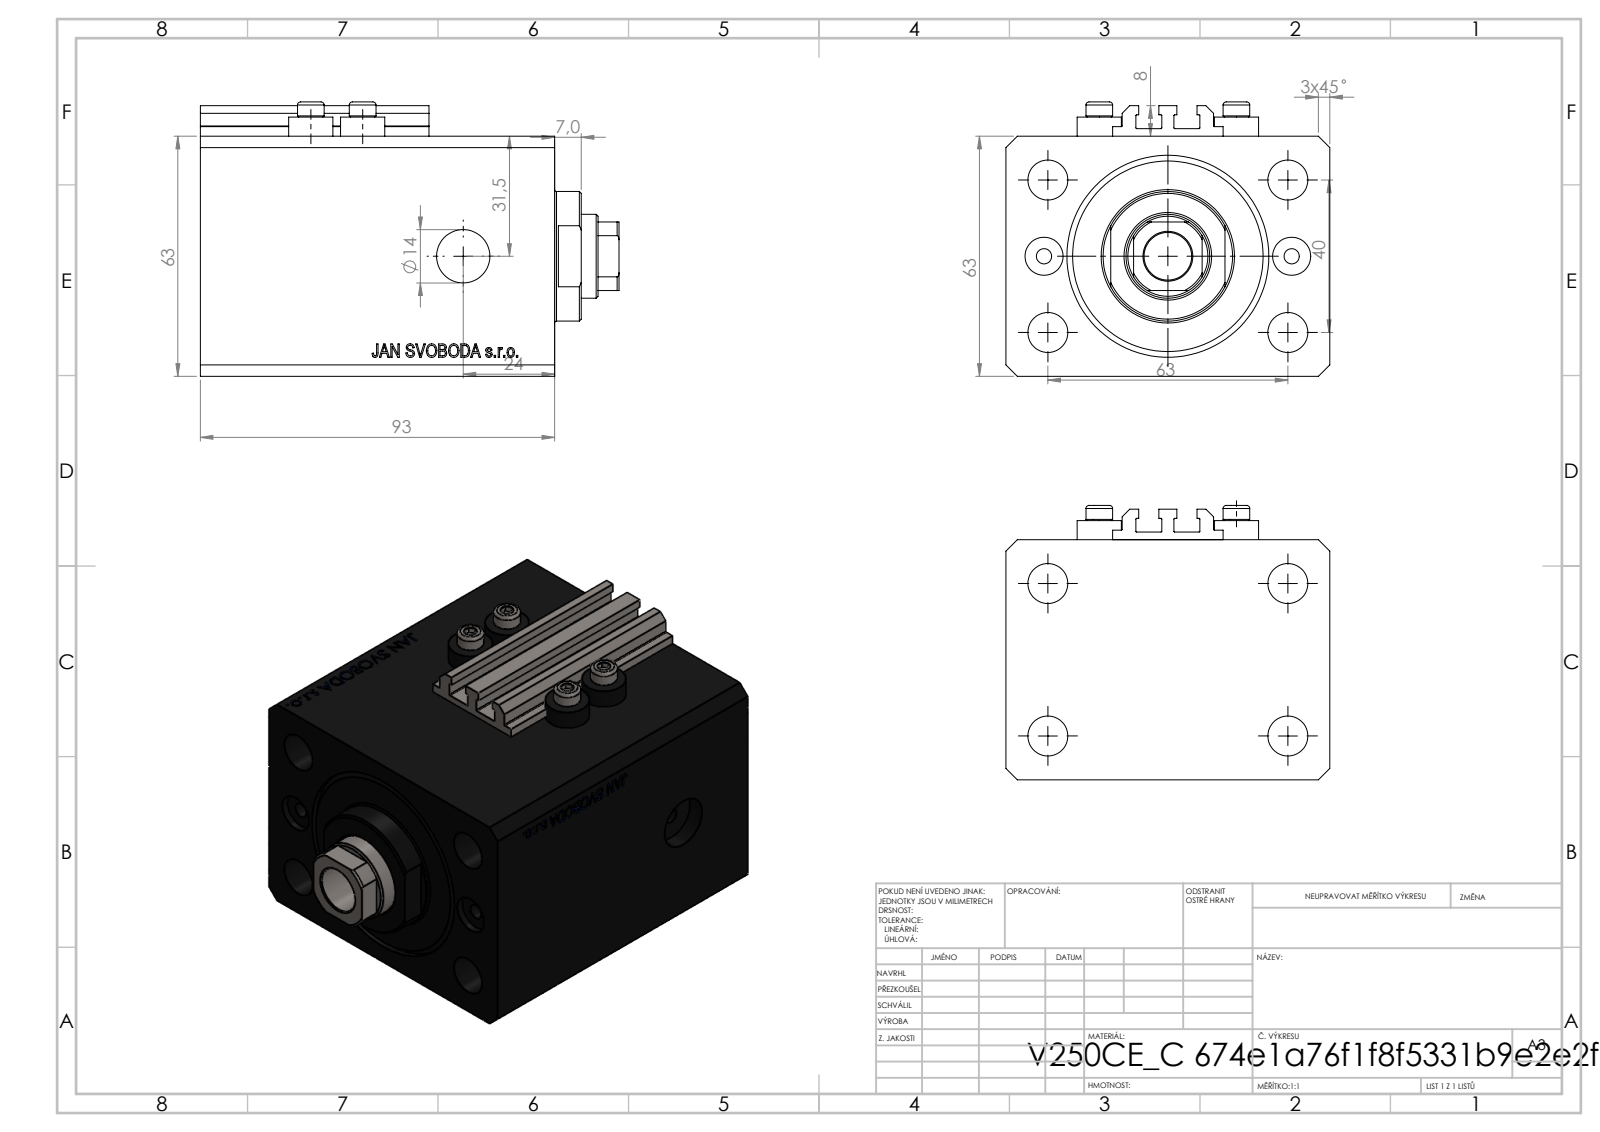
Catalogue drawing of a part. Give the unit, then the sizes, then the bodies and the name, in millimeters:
Units: millimetres
Overall size (bounding box): 110 × 85 × 72
Round holes (diameter × count): ⌀4 ×8, ⌀10.5 ×4, ⌀10 ×2, ⌀14 ×2, ⌀12.5 ×1, ⌀22 ×1, ⌀40 ×1, ⌀53 ×1
Round bosses / shafts (diameter × count): ⌀11.6 ×4, ⌀7 ×4, ⌀34 ×1
Partial cylindrical surfaces — rounded edges, fillets, slot ends (radius × count): R0.2 ×10, R10.5 ×1
Main face-to-face distances: 63, 85, 93, 17, 76, 11.4, 64.6, 81.6, 3, 10
Hole centre spacings: 20.02, 37.31, 67.05, 13.6, 32.5, 36, 38.48, 40
Volume: 460 134 mm³ · Surface area: 92 193 mm²
Bodies: 8 solids, 1034 faces (504 planar, 86 cylindrical, 444 other)
Part name (STEP PRODUCT): V250CE_C_Body; ALLEN BOLT V250CE; V250CE_C_VCP; V250CE_VC_C
STEP written by: SolidWorks 2019 (CONFIG_CONTROL_DESIGN)
